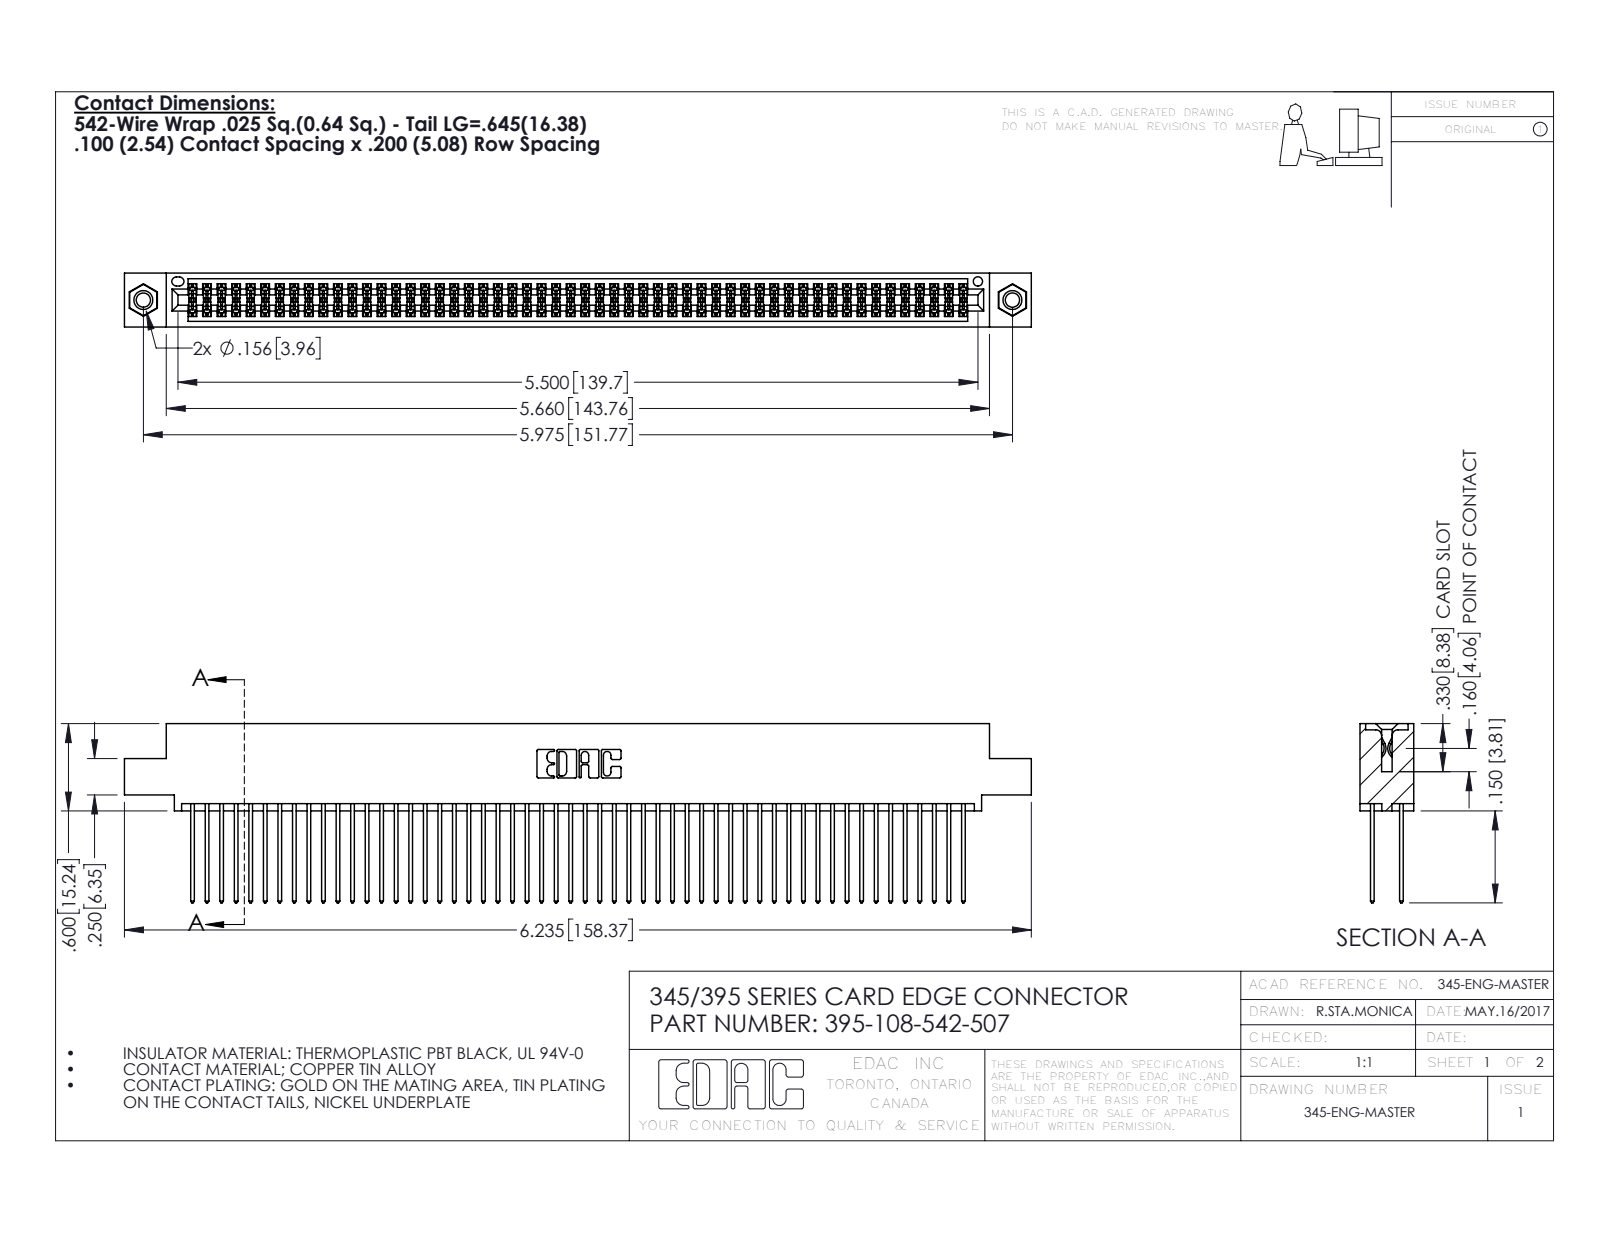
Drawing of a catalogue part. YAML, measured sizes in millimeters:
part_name: "395-108-542-507; 345 Part_0.110 Offset - 0.156 Dia-TI; 345-250-001_345-250-005-103; 345-292-001_345-293-142"
step_written_by: "SolidWorks 2016 (CONFIG_CONTROL_DESIGN)"
units: millimeters
bodies: {solids: 111, faces: 5590, planar: 3680, cylindrical: 1894, other: 16}
overall_size: [158.4, 31.3, 9.4]
volume: 15900
surface_area: 26230
round_holes:
  - {diameter: 2.5, count: 2}
  - {diameter: 3.2, count: 2}
  - {diameter: 4, count: 2}
  - {diameter: 1.6, count: 1}
round_bosses_or_shafts:
  - {diameter: 3.9, count: 2}
partial_cylinders:
  - {radius: 0.2, count: 162}
  - {radius: 0.3, count: 108}
  - {radius: 0.3, count: 22}
  - {radius: 0.2, count: 6}
  - {radius: 0.8, count: 6}
  - {radius: 0.7, count: 3}
  - {radius: 0.4, count: 2}
  - {radius: 0.5, count: 2}
face_to_face_distances: [1.8, 7.6, 5.1, 2.5, 6.9, 0.6, 5.7, 9.4, 4.4, 3.8]
hole_center_spacings: [6.9, 145.8, 151.8]
